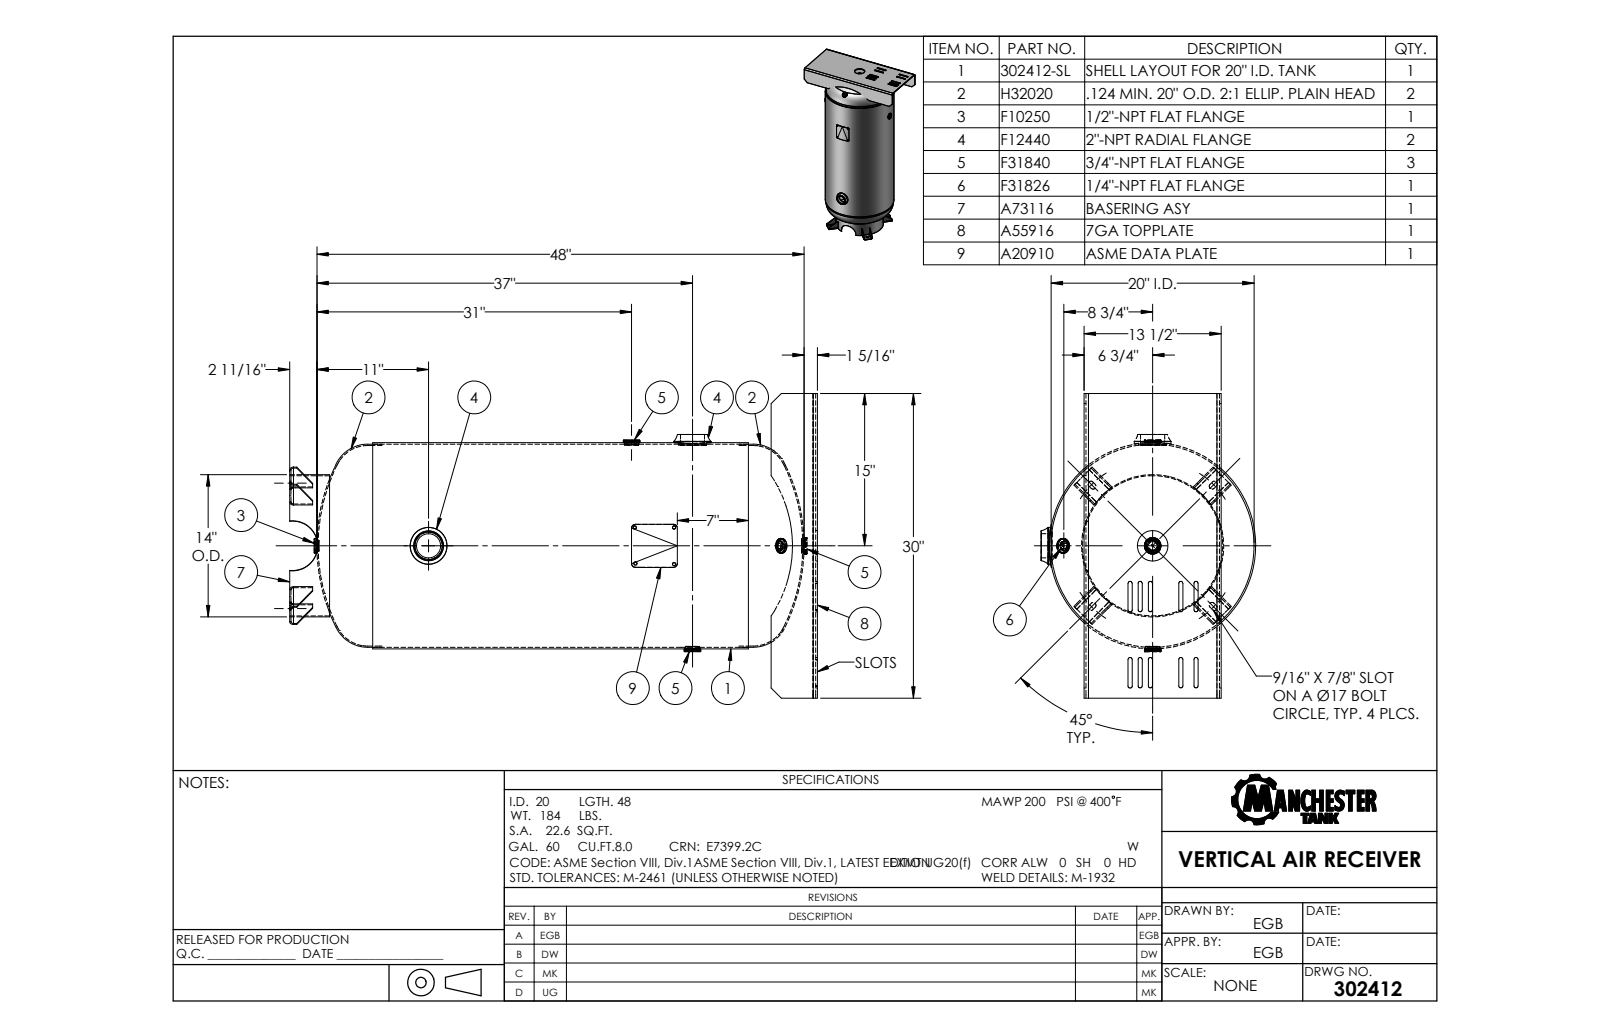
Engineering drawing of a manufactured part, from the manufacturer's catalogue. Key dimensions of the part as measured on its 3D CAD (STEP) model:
Part name (STEP PRODUCT): 302412
STEP written by: SolidWorks 2011 (CONFIG_CONTROL_DESIGN)
Units: inches
Bodies: 0 solids, 308 faces (136 planar, 114 cylindrical, 58 other)
Overall size (bounding box): 51.877 × 30 × 21.14
Round holes (diameter × count): ⌀1.05 ×3, ⌀2.375 ×2, ⌀0.54 ×1, ⌀0.84 ×1, ⌀3 ×1, ⌀13.79 ×1
Round bosses / shafts (diameter × count): ⌀3.625 ×2, ⌀1.63 ×2, ⌀1.45 ×2, ⌀1.438 ×2, ⌀20.308 ×1, ⌀20 ×1, ⌀14 ×1, ⌀1.625 ×1
Partial cylindrical surfaces — rounded edges, fillets, slot ends (radius × count): R0.203 ×20, R0.25 ×8, R0.281 ×8, R0.384 ×8, R0.242 ×2, R0.429 ×2, R7.897 ×2, R10.06 ×1
Main face-to-face distances: 0.187, 13.313, 13.5, 13.126, 0.134, 2.383, 51.877, 51.69, 2.25, 51.743
Hole centre spacings: 6
